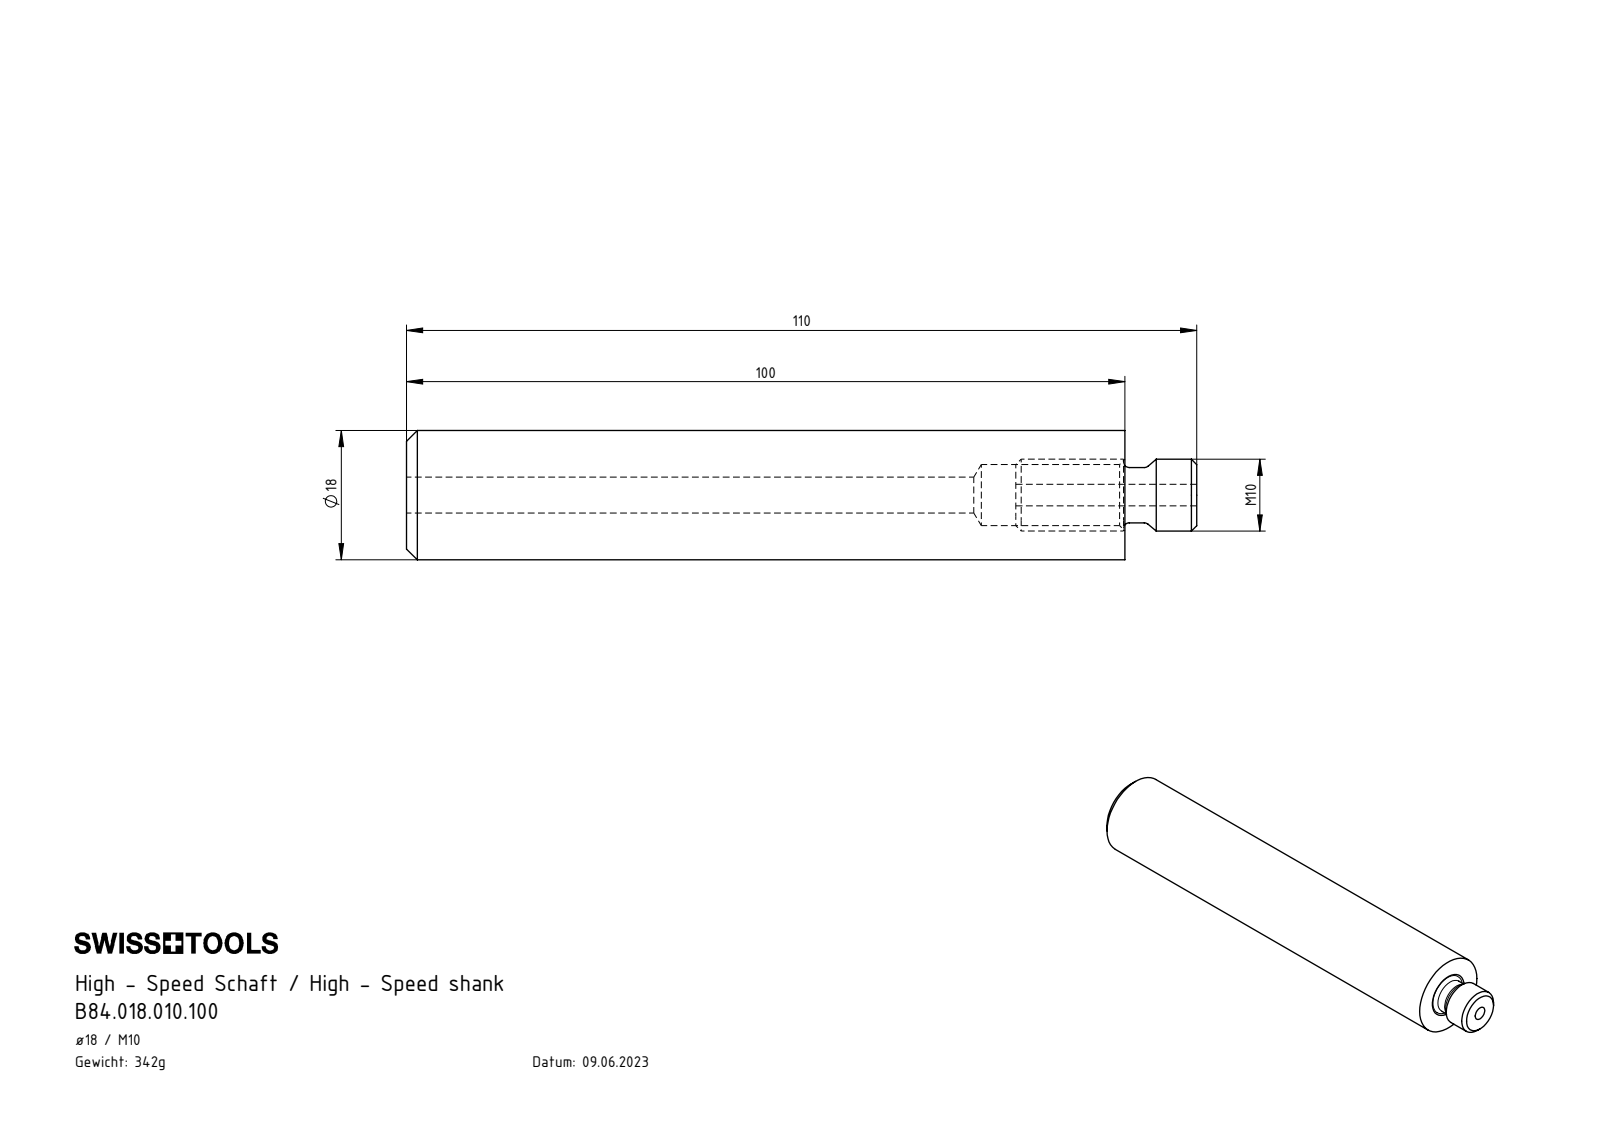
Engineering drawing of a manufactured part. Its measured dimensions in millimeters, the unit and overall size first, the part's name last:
Units: millimetres
Overall size (bounding box): 110 × 18 × 18
Round holes (diameter × count): ⌀3 ×1, ⌀5 ×1, ⌀8.5 ×1
Round bosses / shafts (diameter × count): ⌀18 ×1, ⌀10 ×1, ⌀7.7 ×1
Main face-to-face distances: 100, 110, 10, 84.8, 15.2, 25.2, 99.8, 15, 10.2
Volume: 24 318 mm³ · Surface area: 8 991 mm²
Bodies: 2 solids, 35 faces (5 planar, 14 cylindrical, 16 other)
Part name (STEP PRODUCT): HM1-BG1.010.025_A; HM1-U18.001.100_A; B84.018.010.100
STEP written by: SolidWorks 2022 (CONFIG_CONTROL_DESIGN)
